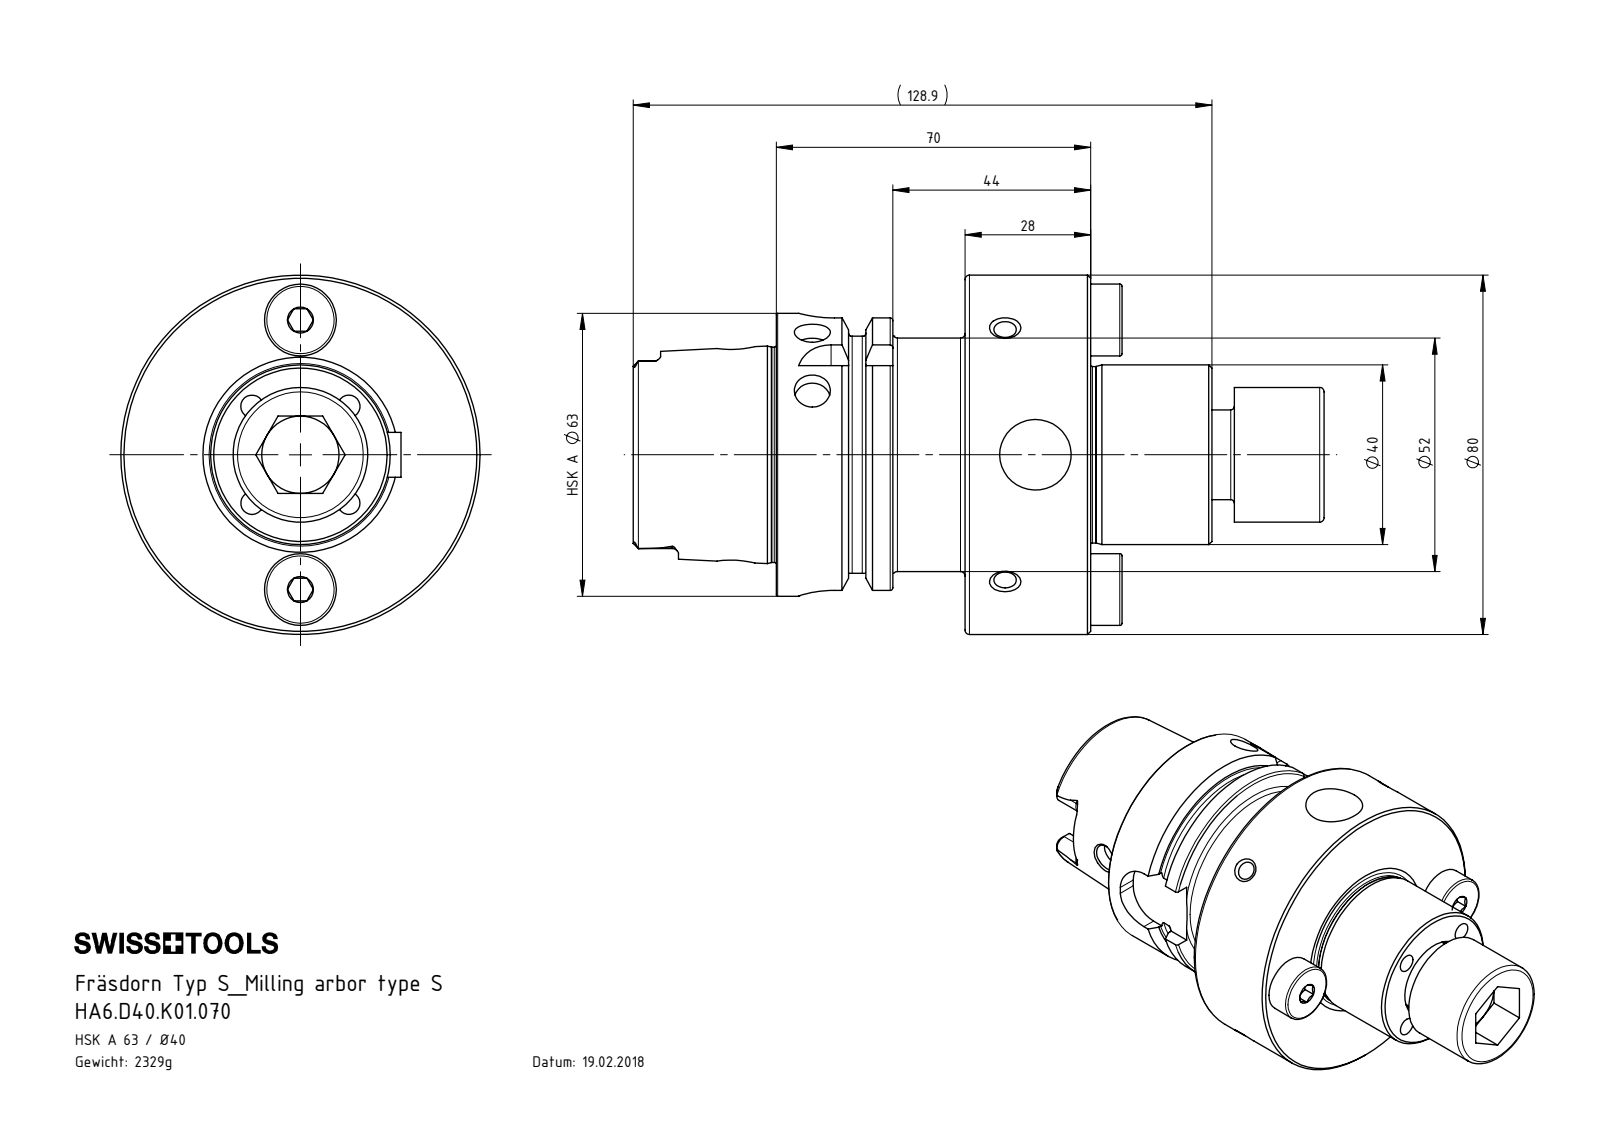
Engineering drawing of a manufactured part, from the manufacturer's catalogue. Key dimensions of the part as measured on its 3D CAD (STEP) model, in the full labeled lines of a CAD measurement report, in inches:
Part name (STEP PRODUCT): DIN 6885 - 10x8x20; HA6-D40.K01.070_D_Fertigbearbeitung; HA6.D40.K01.070; D40-ER1.002.040_A (+1 more)
STEP written by: SolidWorks 2017 (AUTOMOTIVE_DESIGN)
Units: inches
Bodies: 5 solids, 392 faces (97 planar, 120 cylindrical, 175 other)
Overall size (bounding box): 6.059 × 3.15 × 3.15
Volume: 18.1 in³ · Surface area: 91.69 in²
Round holes (diameter × count): ⌀0.197 ×12, ⌀0.315 ×2, ⌀0.551 ×2, ⌀0.295 ×1, ⌀0.331 ×1, ⌀0.394 ×1, ⌀0.669 ×1, ⌀0.689 ×1, ⌀0.748 ×1, ⌀0.827 ×1, ⌀1.339 ×1, ⌀1.575 ×1
Round bosses / shafts (diameter × count): ⌀0.63 ×2, ⌀0.236 ×2, ⌀0.181 ×2, ⌀3.15 ×1, ⌀2.48 ×1, ⌀2.163 ×1, ⌀2.047 ×1, ⌀1.887 ×1
Partial cylindrical surfaces — rounded edges, fillets, slot ends (radius × count): R0.055 ×6, R0.113 ×4, R0.197 ×4, R0.315 ×4
Main face-to-face distances: 1.102, 1.654, 2.756, 0.787, 2.165, 0.984, 3.819, 1.063, 1.734, 2.362
Hole centre spacings: 0.317, 0.6, 0.849, 0.868, 1.661, 1.181, 1.2, 2.362
